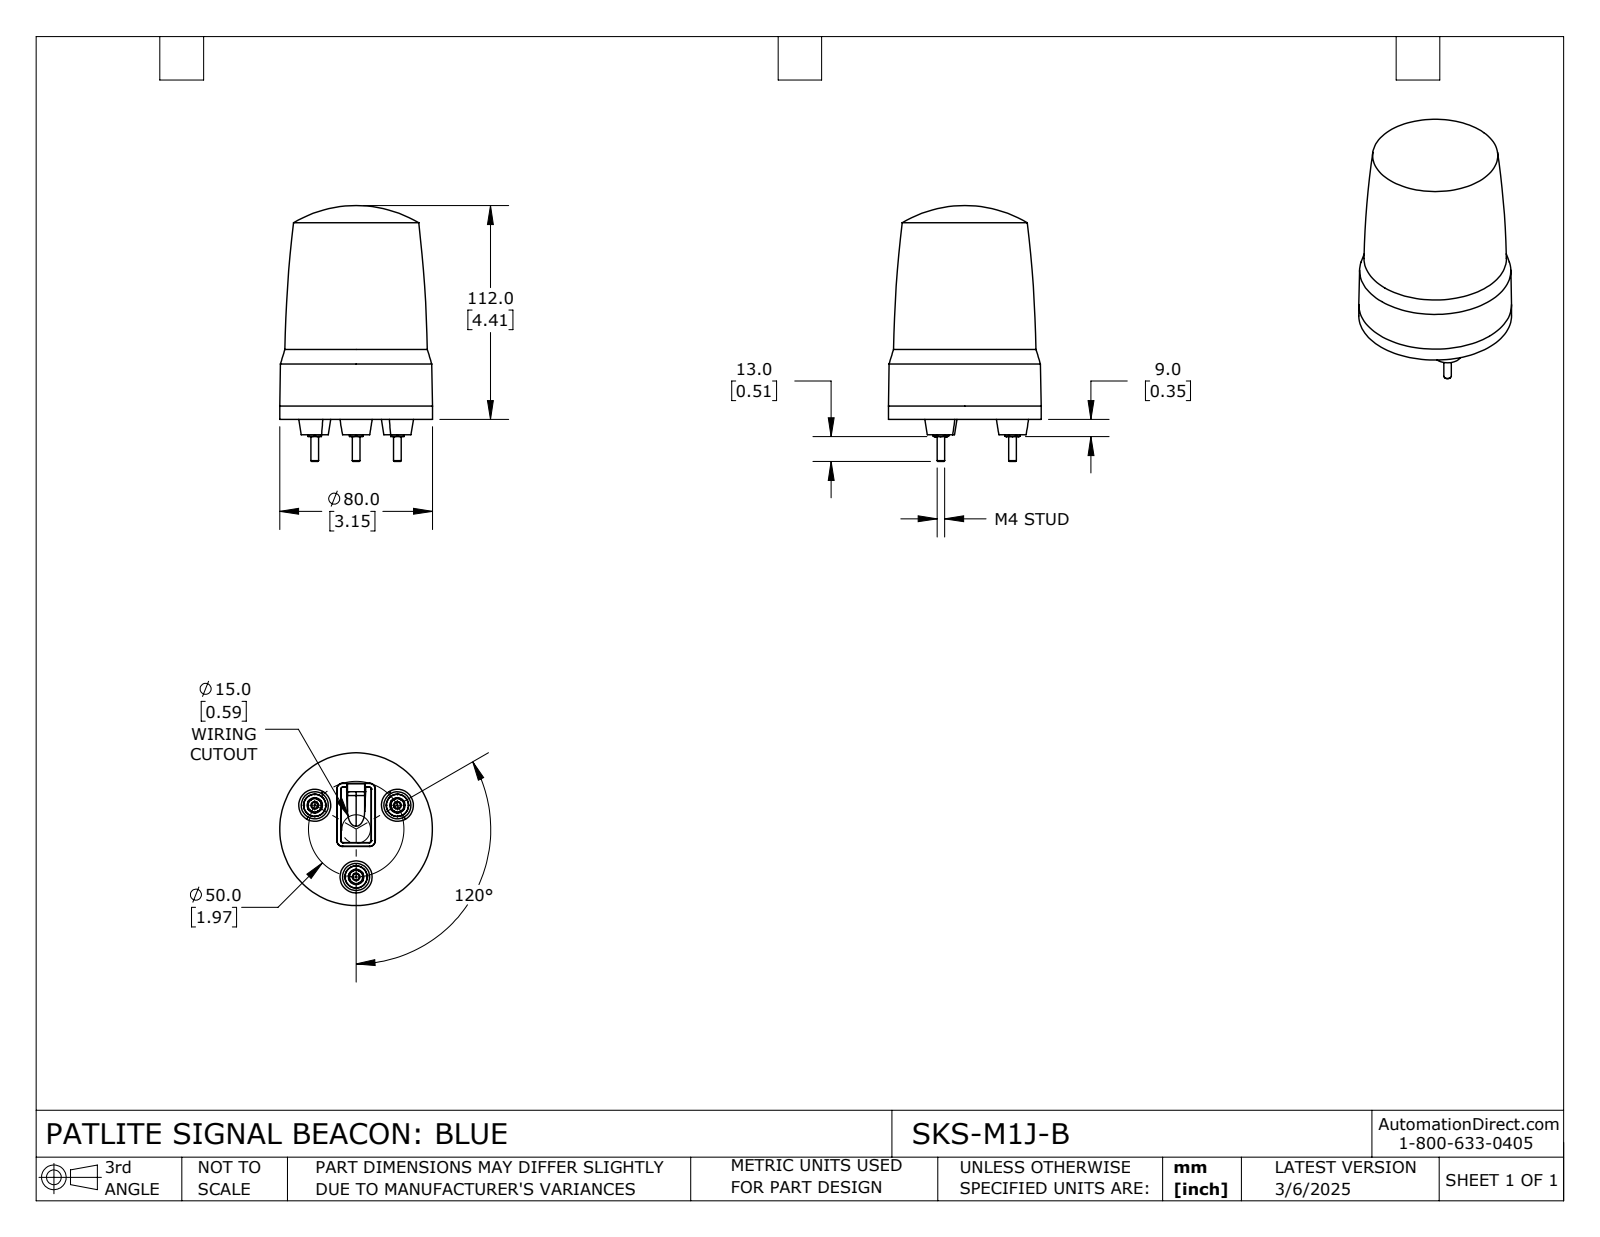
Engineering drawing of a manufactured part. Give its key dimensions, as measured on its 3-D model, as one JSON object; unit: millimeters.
{"part_name": "SKS-M1J-B", "step_written_by": "SolidWorks 2024 (CONFIG_CONTROL_DESIGN)", "units": "millimeters", "bodies": {"solids": 1, "faces": 138, "planar": 47, "cylindrical": 14, "other": 77}, "overall_size": [134, 80, 80], "volume_mm3": 463225, "surface_area_mm2": 35408, "round_bosses_or_shafts": [[8, 3], [4, 3], [80, 1]], "face_to_face_distances": [0.85, 2.45, 1.6, 5.3, 6.15, 7.75, 2.7, 8, 8.85, 10.45]}
